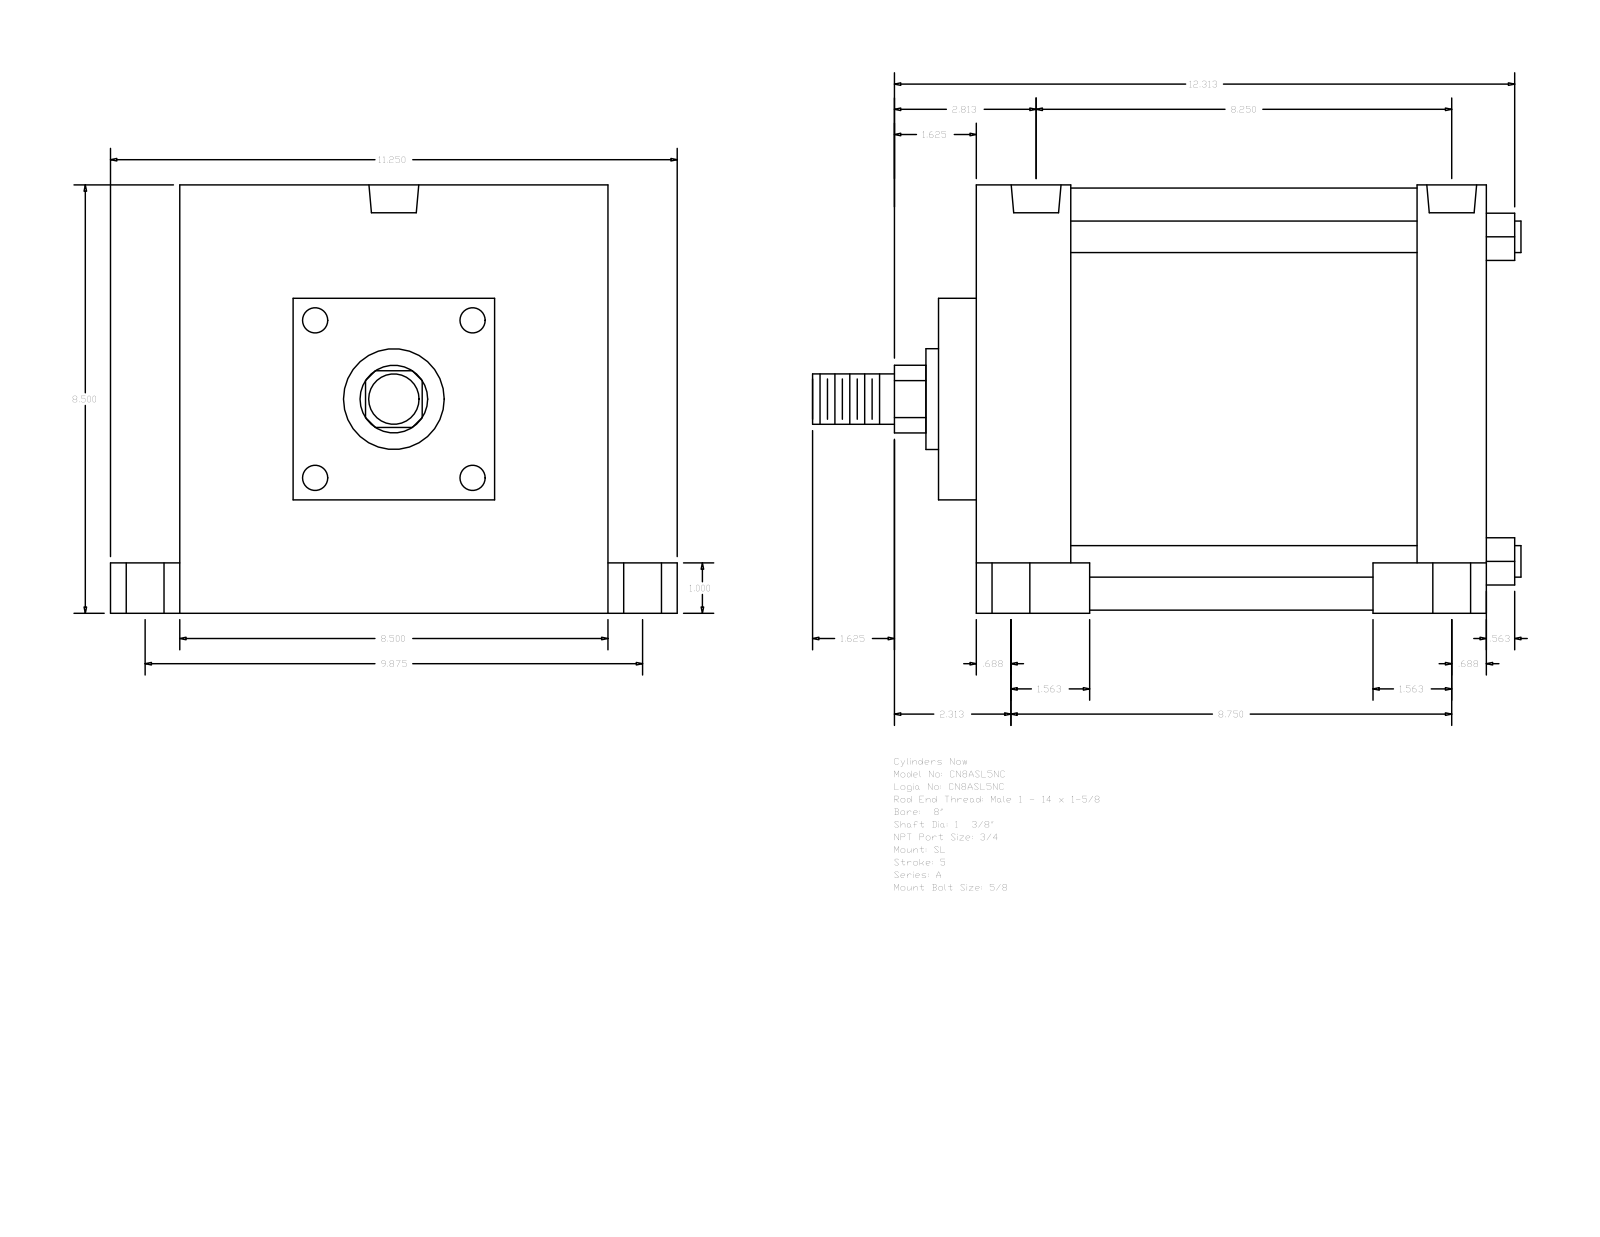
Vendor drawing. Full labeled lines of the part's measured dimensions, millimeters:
Part name (STEP PRODUCT): A_SL__0800_1.375
STEP written by: GSSL Pune (CONFIG_CONTROL_DESIGN)
Units: millimetres
Bodies: 0 solids, 117 faces (85 planar, 32 cylindrical, 0 other)
Overall size (bounding box): 357.19 × 285.75 × 215.9
Round holes (diameter × count): ⌀15.08 ×4, ⌀19.05 ×4, ⌀25.4 ×4, ⌀25.12 ×2
Round bosses / shafts (diameter × count): ⌀15.88 ×4, ⌀212.72 ×1, ⌀50.8 ×1, ⌀34.92 ×1, ⌀25.4 ×1
Partial cylindrical surfaces — rounded edges, fillets, slot ends (radius × count): R17.06 ×1
Main face-to-face distances: 257.18, 215.9, 34.93, 57.15, 47.63, 209.55, 222.25, 174.62, 19.04, 66.67
Hole centre spacings: 6.35, 125.41, 125.57, 126.05, 126.85, 196.85, 203.2, 222.25
